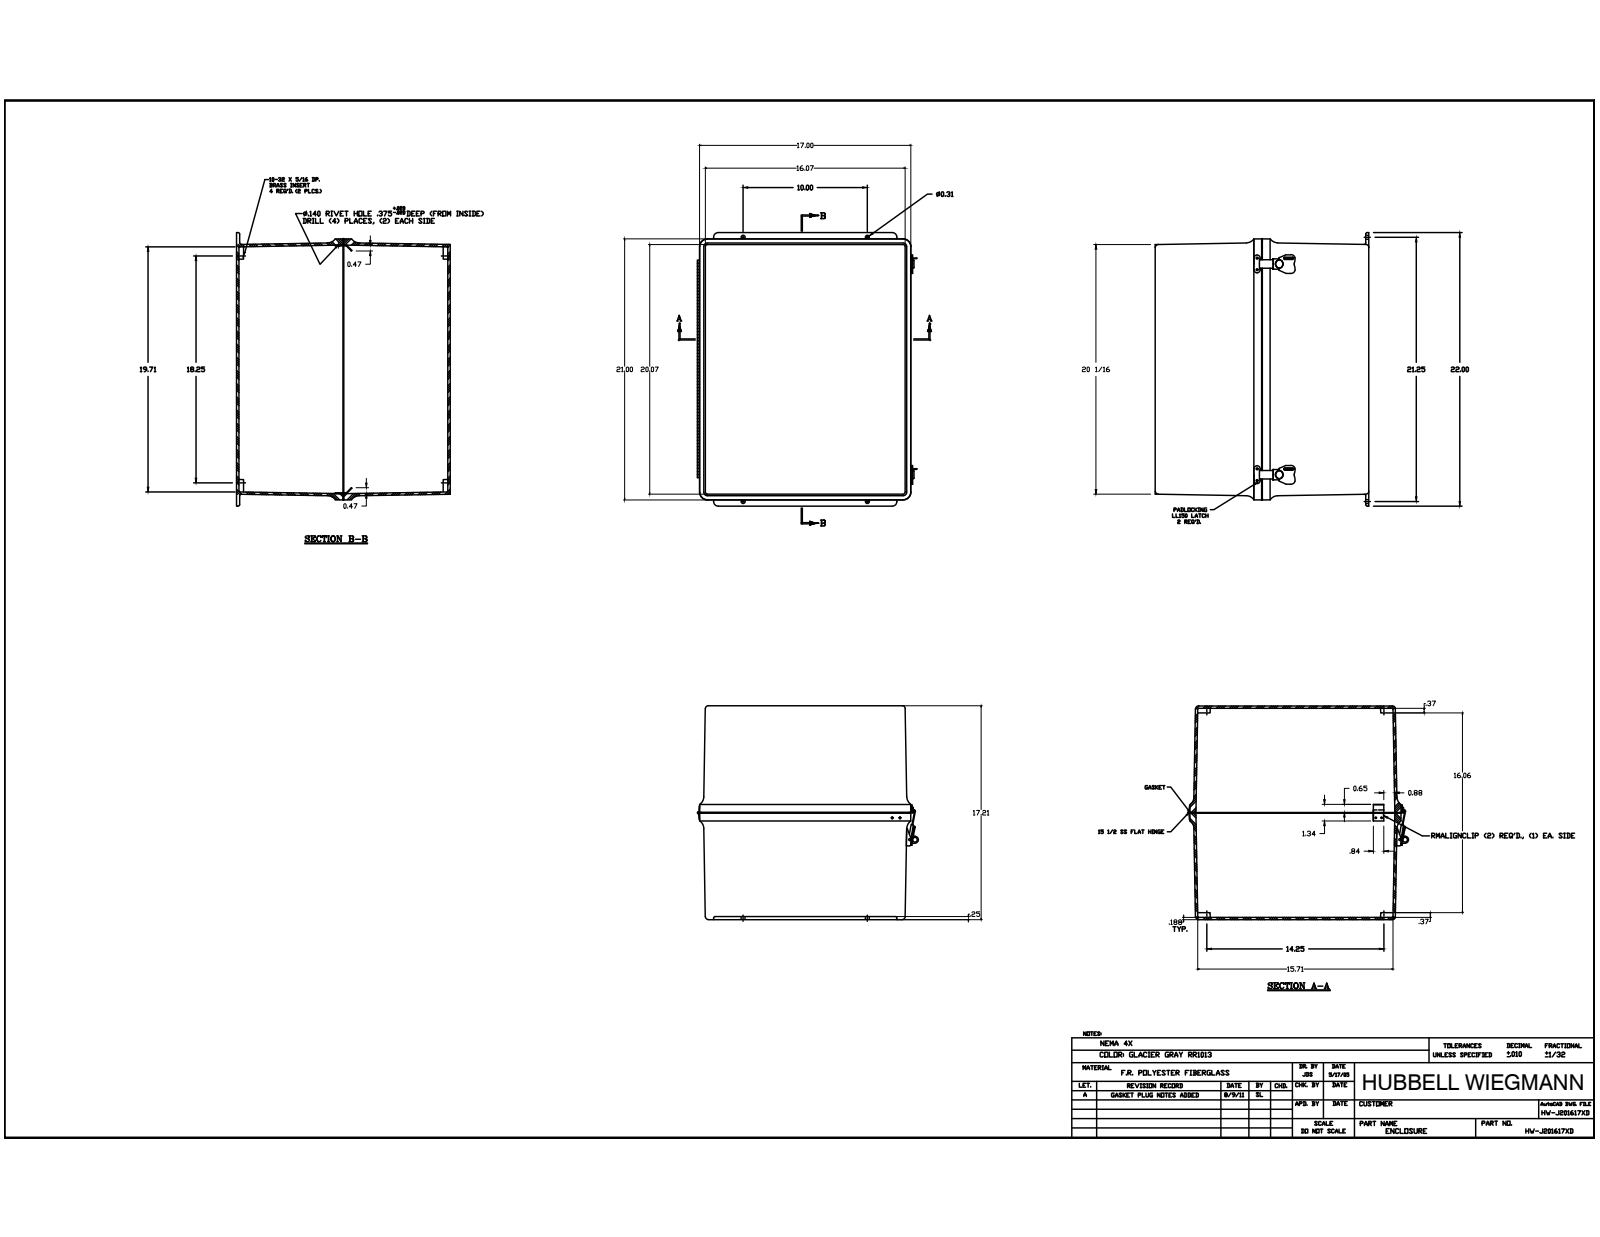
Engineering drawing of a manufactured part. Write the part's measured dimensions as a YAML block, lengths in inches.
part_name: "J2016SSH; RMINS45821P_153; RMINS45821P_154; RMINS45821P_155 (+8 more)"
step_written_by: "Autodesk Inventor 2014 (AUTOMOTIVE_DESIGN)"
units: inches
bodies: {solids: 62, faces: 1763, planar: 734, cylindrical: 689, other: 340}
overall_size: [22, 17.741, 17.184]
volume: 392.8
surface_area: 3982
round_holes:
  - {diameter: 0.14, count: 26}
  - {diameter: 0.136, count: 12}
  - {diameter: 0.152, count: 11}
  - {diameter: 0.156, count: 7}
  - {diameter: 0.13, count: 4}
  - {diameter: 0.165, count: 4}
  - {diameter: 0.197, count: 4}
  - {diameter: 0.218, count: 4}
  - {diameter: 0.118, count: 2}
  - {diameter: 0.138, count: 2}
  - {diameter: 0.193, count: 2}
  - {diameter: 0.531, count: 2}
round_bosses_or_shafts:
  - {diameter: 0.25, count: 24}
  - {diameter: 0.125, count: 24}
  - {diameter: 0.27, count: 7}
  - {diameter: 0.583, count: 2}
  - {diameter: 0.524, count: 2}
  - {diameter: 0.209, count: 2}
  - {diameter: 0.185, count: 2}
  - {diameter: 0.128, count: 2}
partial_cylinders:
  - {radius: 0.031, count: 88}
  - {radius: 0.079, count: 19}
  - {radius: 0.25, count: 16}
  - {radius: 0.75, count: 14}
  - {radius: 0.037, count: 8}
  - {radius: 0.039, count: 8}
  - {radius: 0.047, count: 8}
  - {radius: 0.063, count: 8}
face_to_face_distances: [0.187, 16.189, 20.189, 16.001, 17.184, 0.188, 16.997, 16.809, 16.996, 16.376]
hole_center_spacings: [3.75, 11, 17, 3.812, 7.25, 7.5, 14.75, 24.526]
